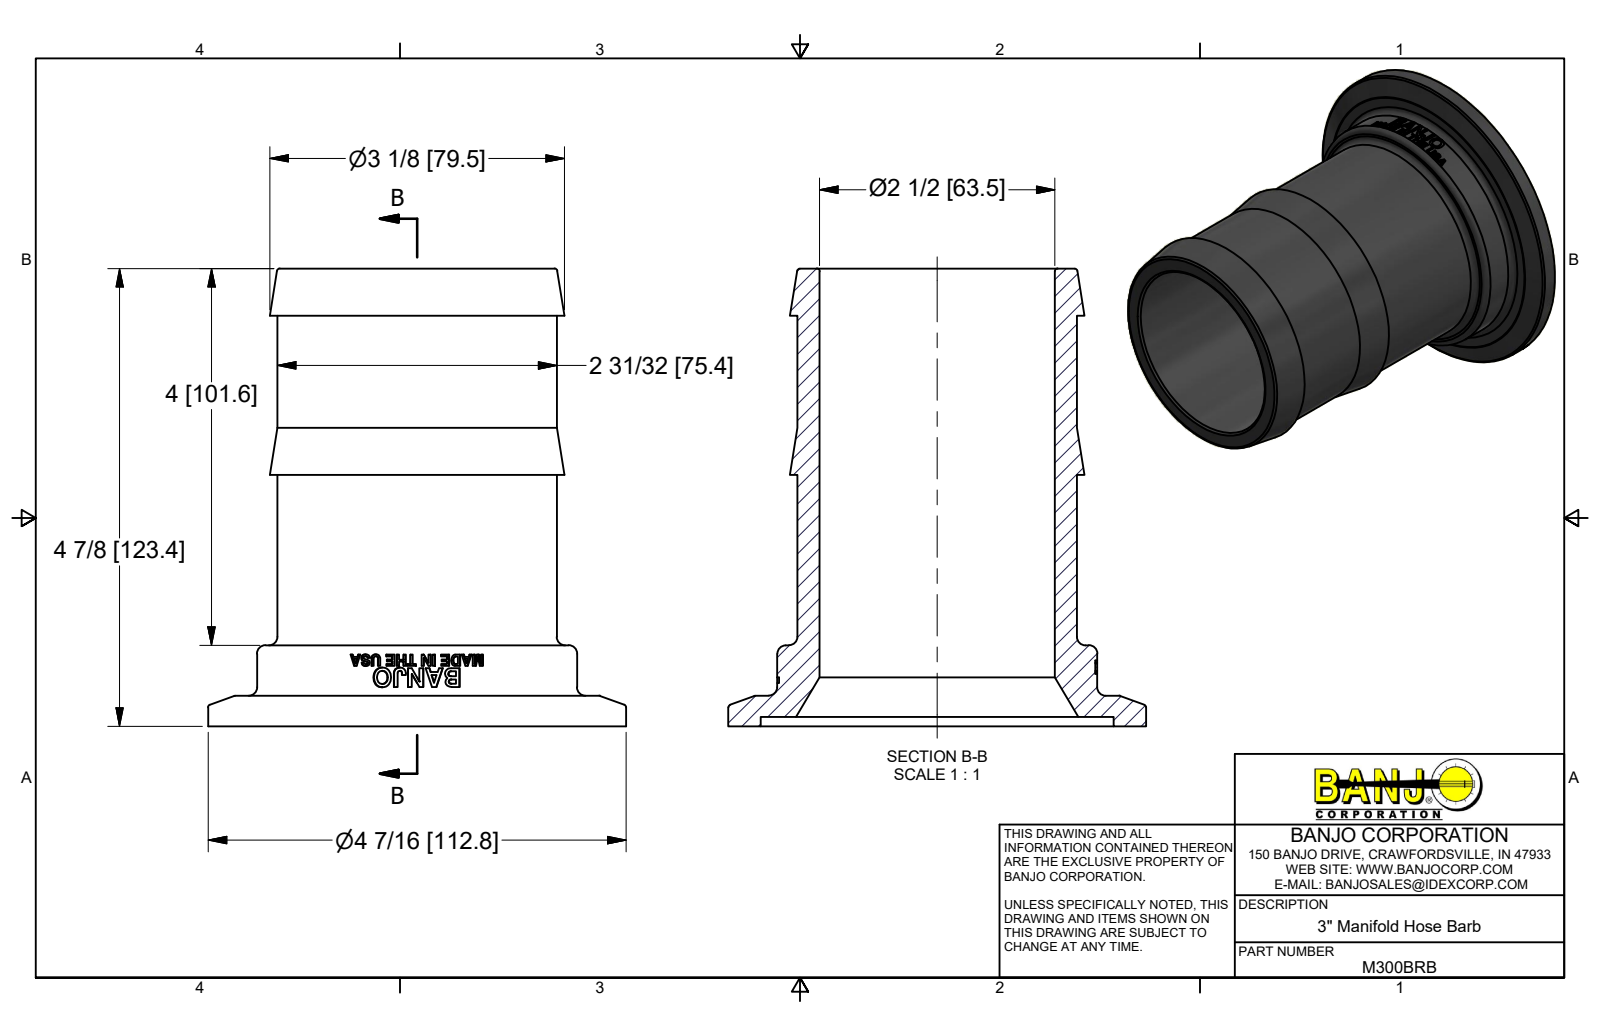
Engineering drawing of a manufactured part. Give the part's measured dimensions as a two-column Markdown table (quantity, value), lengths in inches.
| quantity | value |
| --- | --- |
| part name | M300BRB |
| STEP written by | Autodesk Inventor 2018 (AUTOMOTIVE_DESIGN) |
| units | inches |
| bodies | 1 solid, 381 faces (165 planar, 44 cylindrical, 172 other) |
| overall size | 4.86 × 4.44 × 4.44 |
| volume | 12.88 in³ |
| surface area | 105.7 in² |
| round holes (diameter × count) | 2.5 × 1, 3.75 × 1 |
| round bosses / shafts (diameter × count) | 4.44 × 1, 3.4 × 1, 2.97 × 1 |
| partial cylindrical surfaces (radius × count) | 1.68 × 1 |
| main face-to-face distances | 0.1, 0.224, 0.324, 4.86, 4.76, 4.535, 2.67, 4.36, 2.57, 4.26 |
